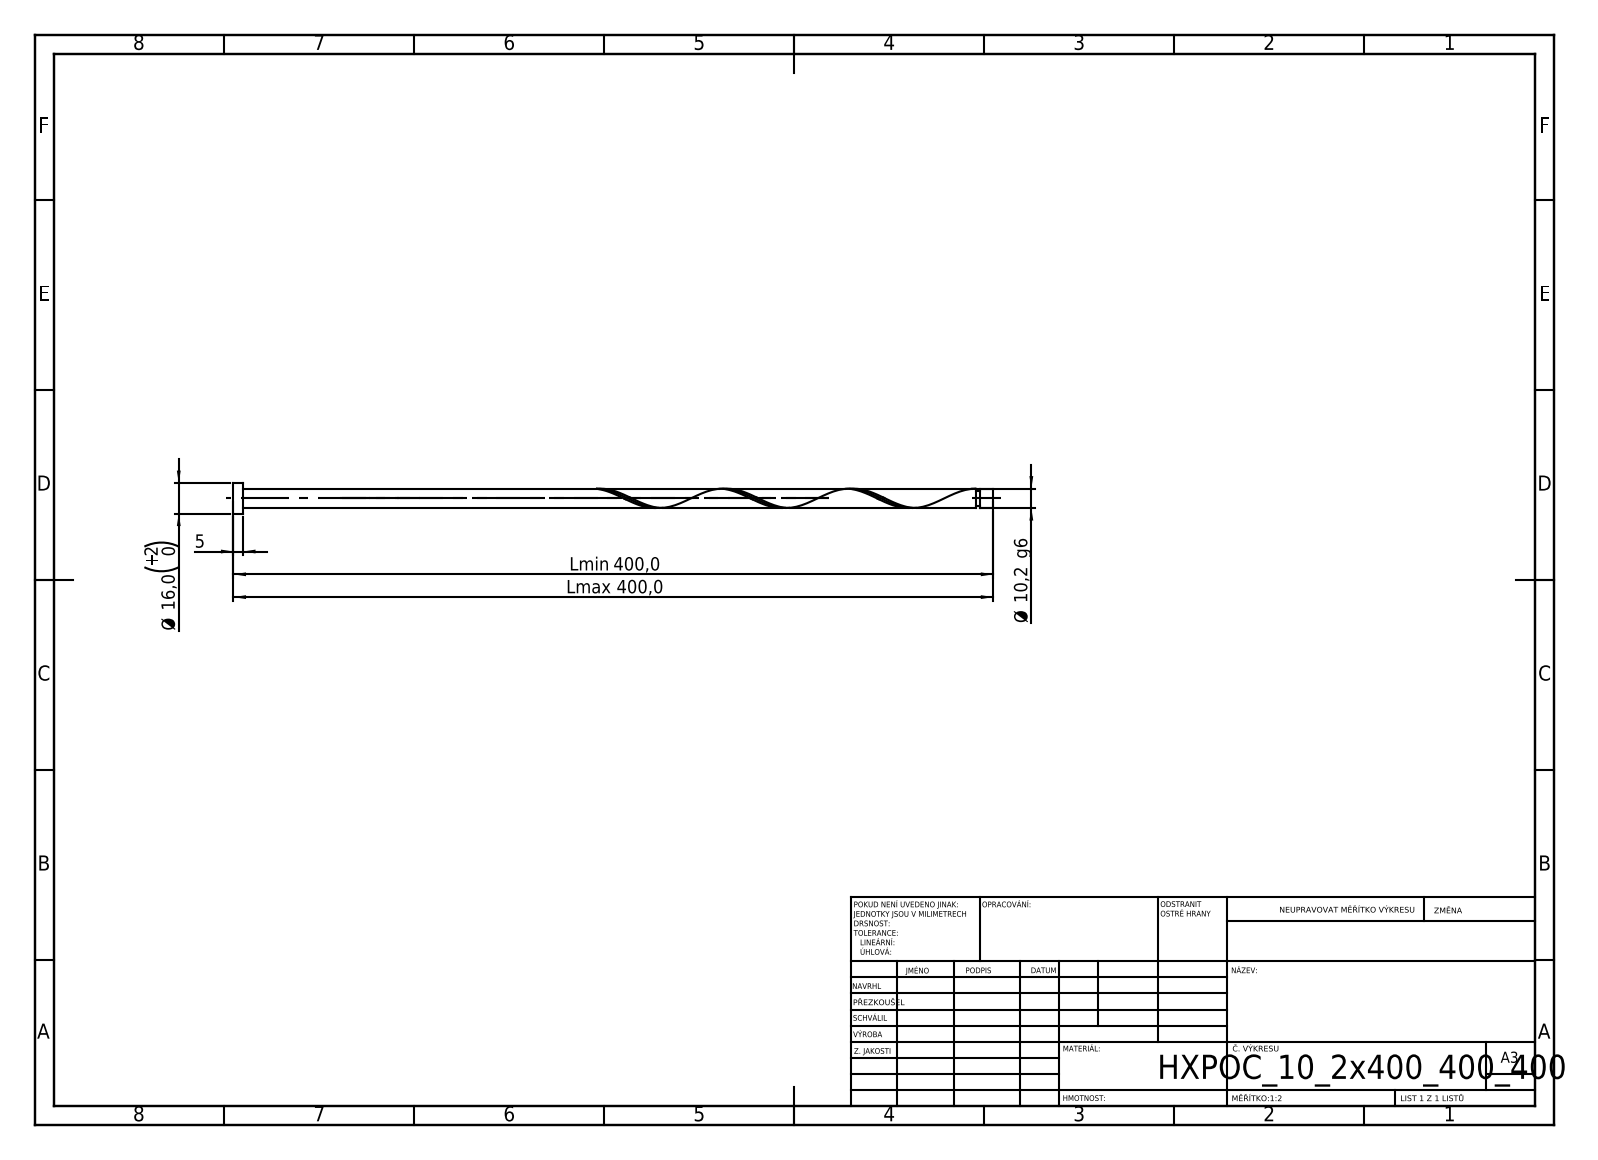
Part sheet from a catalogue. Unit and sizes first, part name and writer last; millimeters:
Units: millimetres
Overall size (bounding box): 400 × 16 × 16
Round bosses / shafts (diameter × count): ⌀16 ×1, ⌀10.2 ×1, ⌀8.16 ×1
Main face-to-face distances: 5, 400, 395, 392.89, 387.89, 7.11, 390.85, 385.85, 2.04, 9.15
Volume: 32 909 mm³ · Surface area: 13 579 mm²
Bodies: 1 solid, 21 faces (6 planar, 14 cylindrical, 1 other)
STEP written by: SolidWorks 2019 (CONFIG_CONTROL_DESIGN)
